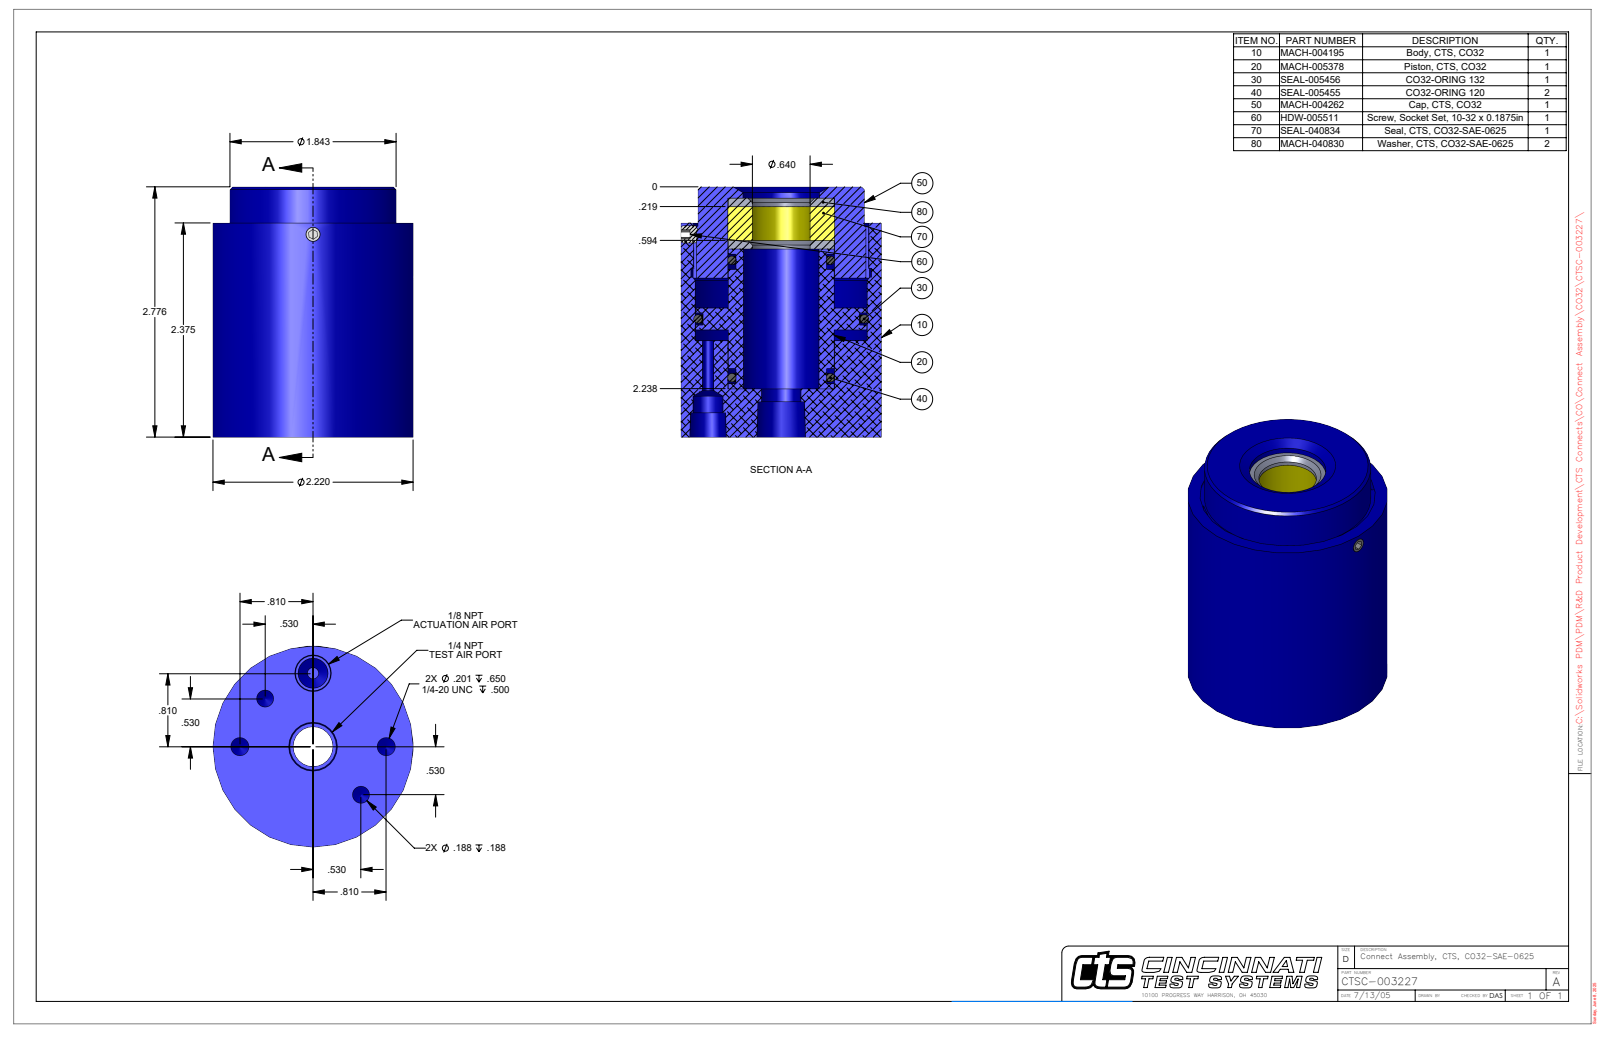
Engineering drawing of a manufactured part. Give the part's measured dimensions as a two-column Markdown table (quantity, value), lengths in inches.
| quantity | value |
| --- | --- |
| part name | CTSC-003227 |
| STEP written by | SolidWorks 2023 (AUTOMOTIVE_DESIGN) |
| units | inches |
| bodies | 1 solid, 118 faces (49 planar, 44 cylindrical, 25 other) |
| overall size | 2.776 × 2.22 × 2.22 |
| volume | 8.916 in³ |
| surface area | 35.49 in² |
| round holes (diameter × count) | 0.187 × 2, 0.201 × 2, 0.094 × 1, 0.125 × 1, 0.159 × 1, 0.332 × 1, 0.438 × 1, 0.64 × 1, 0.837 × 1, 0.848 × 1, 1.182 × 1, 1.943 × 1 |
| round bosses / shafts (diameter × count) | 2.22 × 1, 1.843 × 1, 1.172 × 1 |
| partial cylindrical surfaces (radius × count) | 0.095 × 1, 1.092 × 1 |
| main face-to-face distances | 2.776, 2.375, 0.401, 0.537, 1.837, 2.238, 2.338, 1.8, 0.037, 0.438 |
| hole center spacings | 0.6, 0.81, 1.441, 0.75, 1.145, 1.5, 1.62 |
